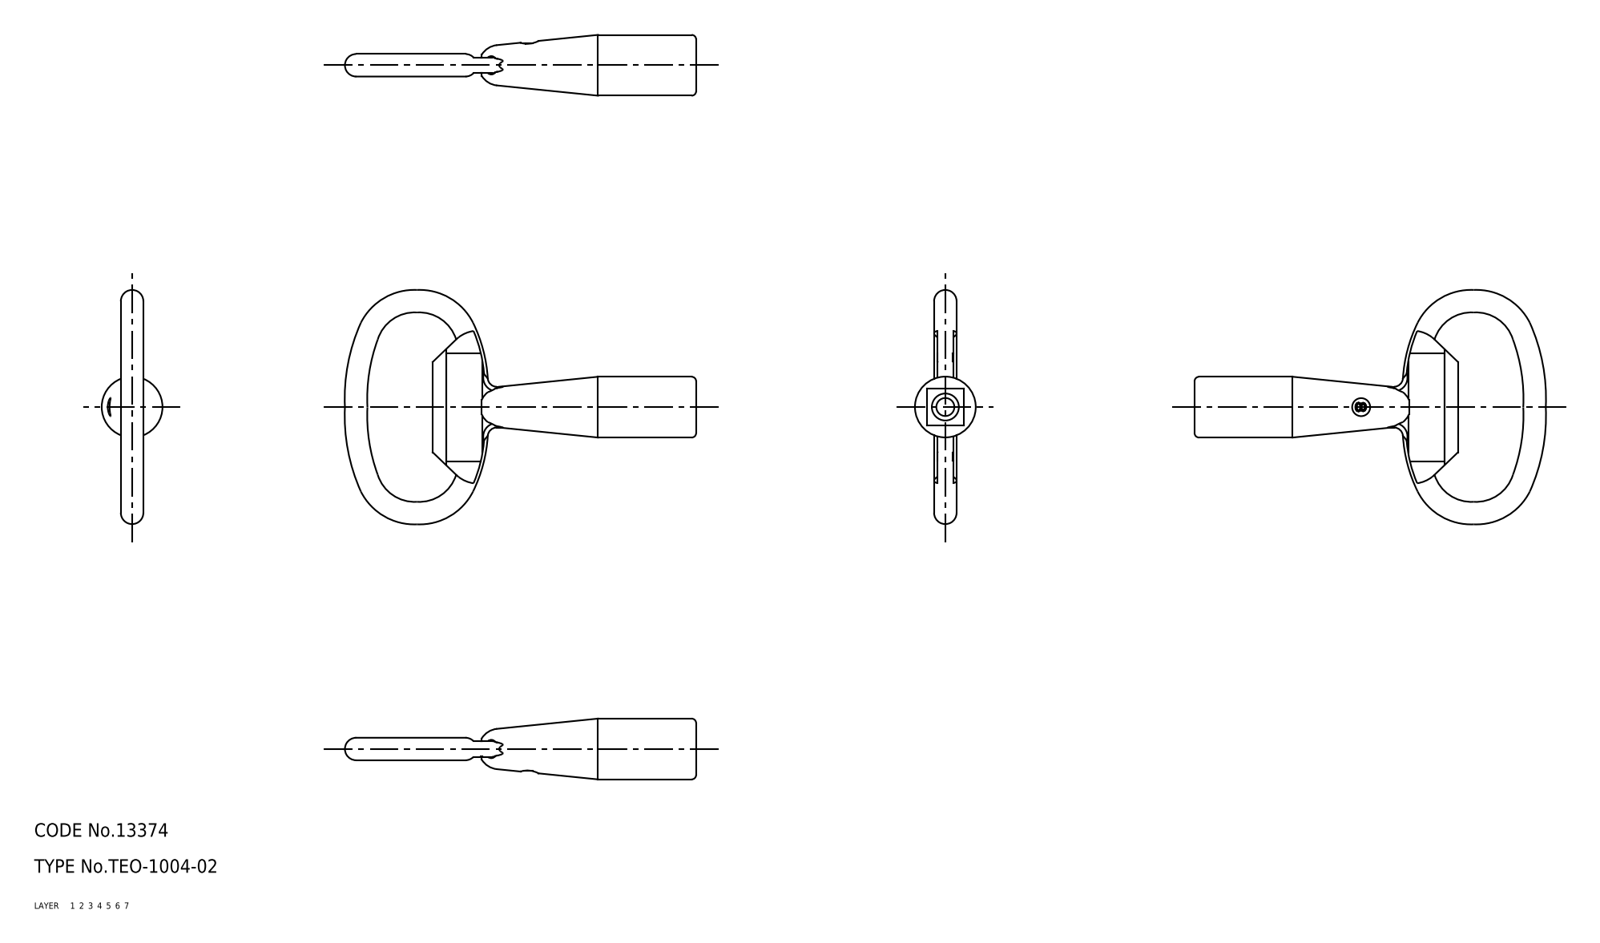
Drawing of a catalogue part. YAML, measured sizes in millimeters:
part_name: "key"
step_written_by: "CADfix (AUTOMOTIVE_DESIGN)"
units: millimeters
bodies: {solids: 1, faces: 57, planar: 0, cylindrical: 0, other: 57}
overall_size: [78, 52, 13.5]
volume: 7299
surface_area: 4726
